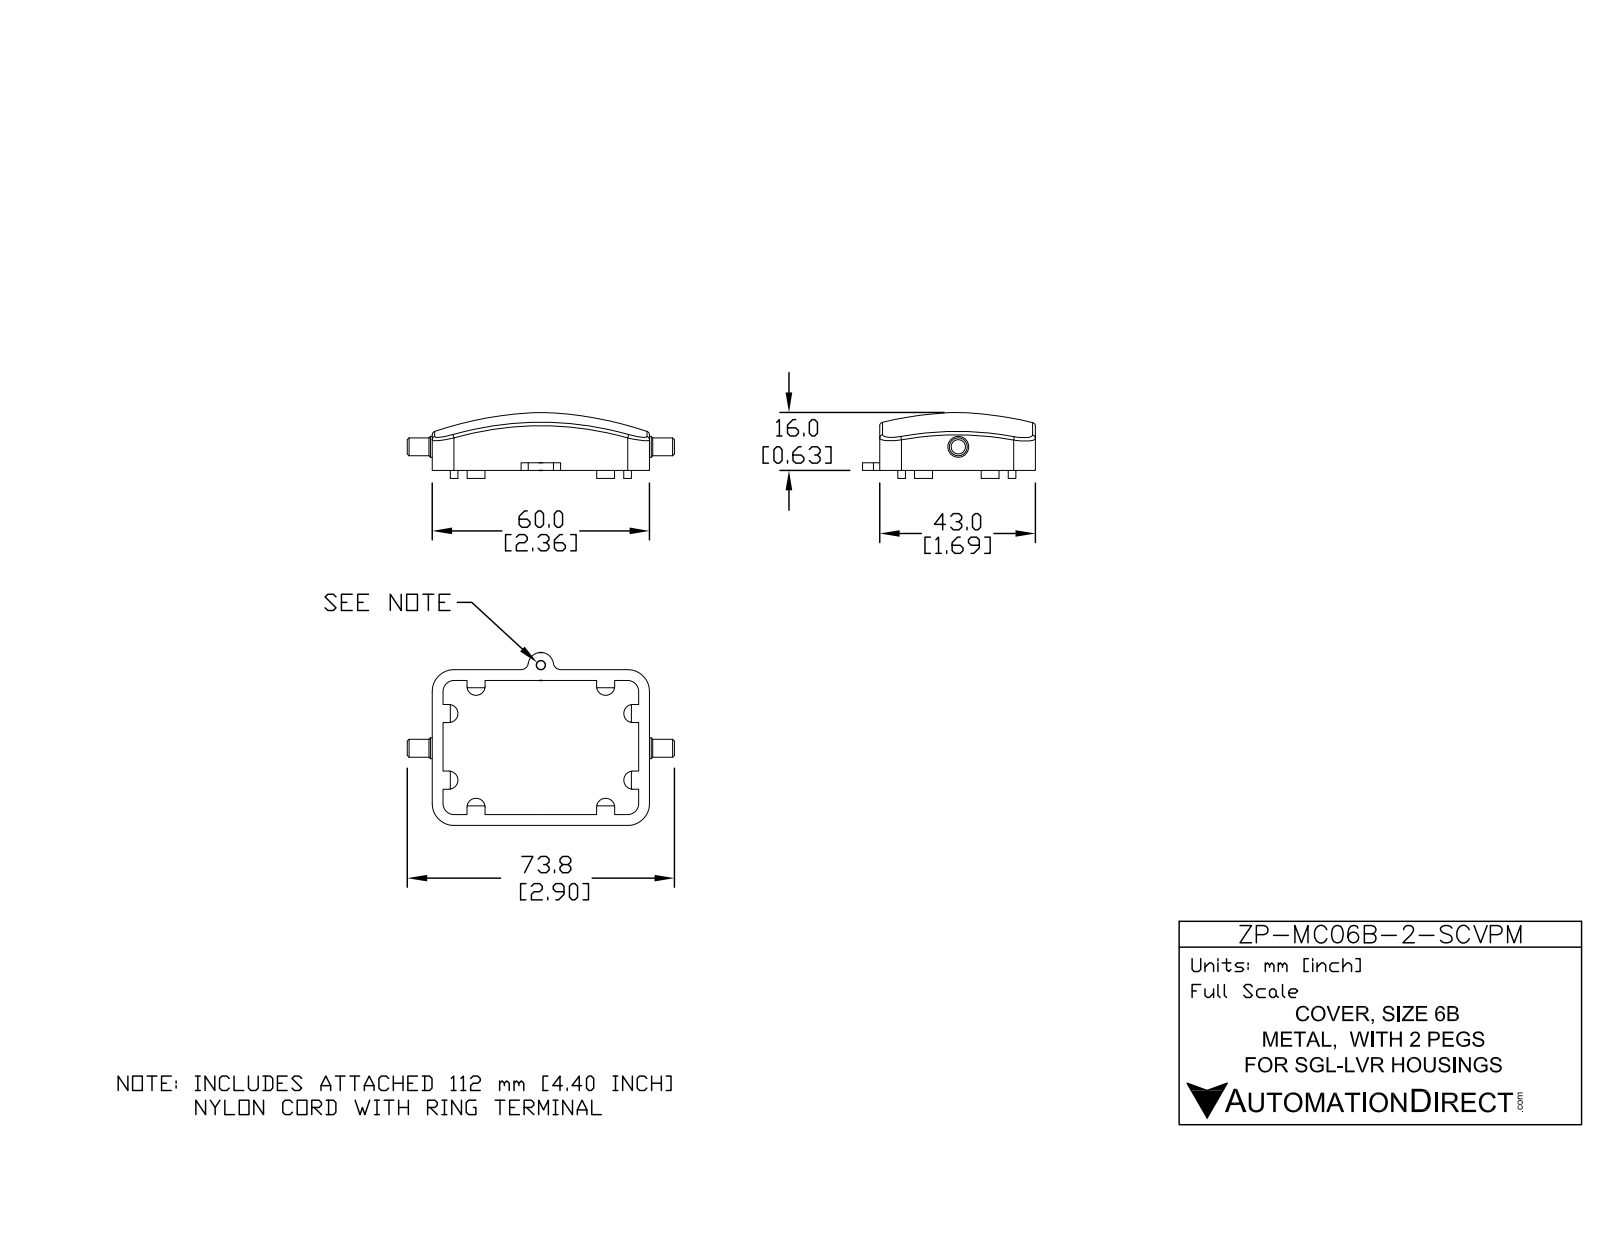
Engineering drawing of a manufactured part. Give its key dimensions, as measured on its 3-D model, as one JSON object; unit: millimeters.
{"part_name": "ZP-MC06B-2-SCVPM", "step_written_by": "SolidWorks 2014 (AUTOMOTIVE_DESIGN)", "units": "millimeters", "bodies": {"solids": 4, "faces": 137, "planar": 71, "cylindrical": 42, "other": 24}, "overall_size": [146.44, 73.78, 65.1], "volume_mm3": 14367, "surface_area_mm2": 10823, "round_holes": [[2.5, 1], [4.1, 1]], "round_bosses_or_shafts": [[5.77, 1], [4.95, 1]], "partial_cylinders_radius": [[2.5, 8], [6, 6], [0.45, 4], [3, 4], [0.6, 2], [2, 2], [3.5, 1], [3.92, 1]], "face_to_face_distances": [3, 40, 43, 37, 57, 60, 5, 9.6, 54, 45.4]}
